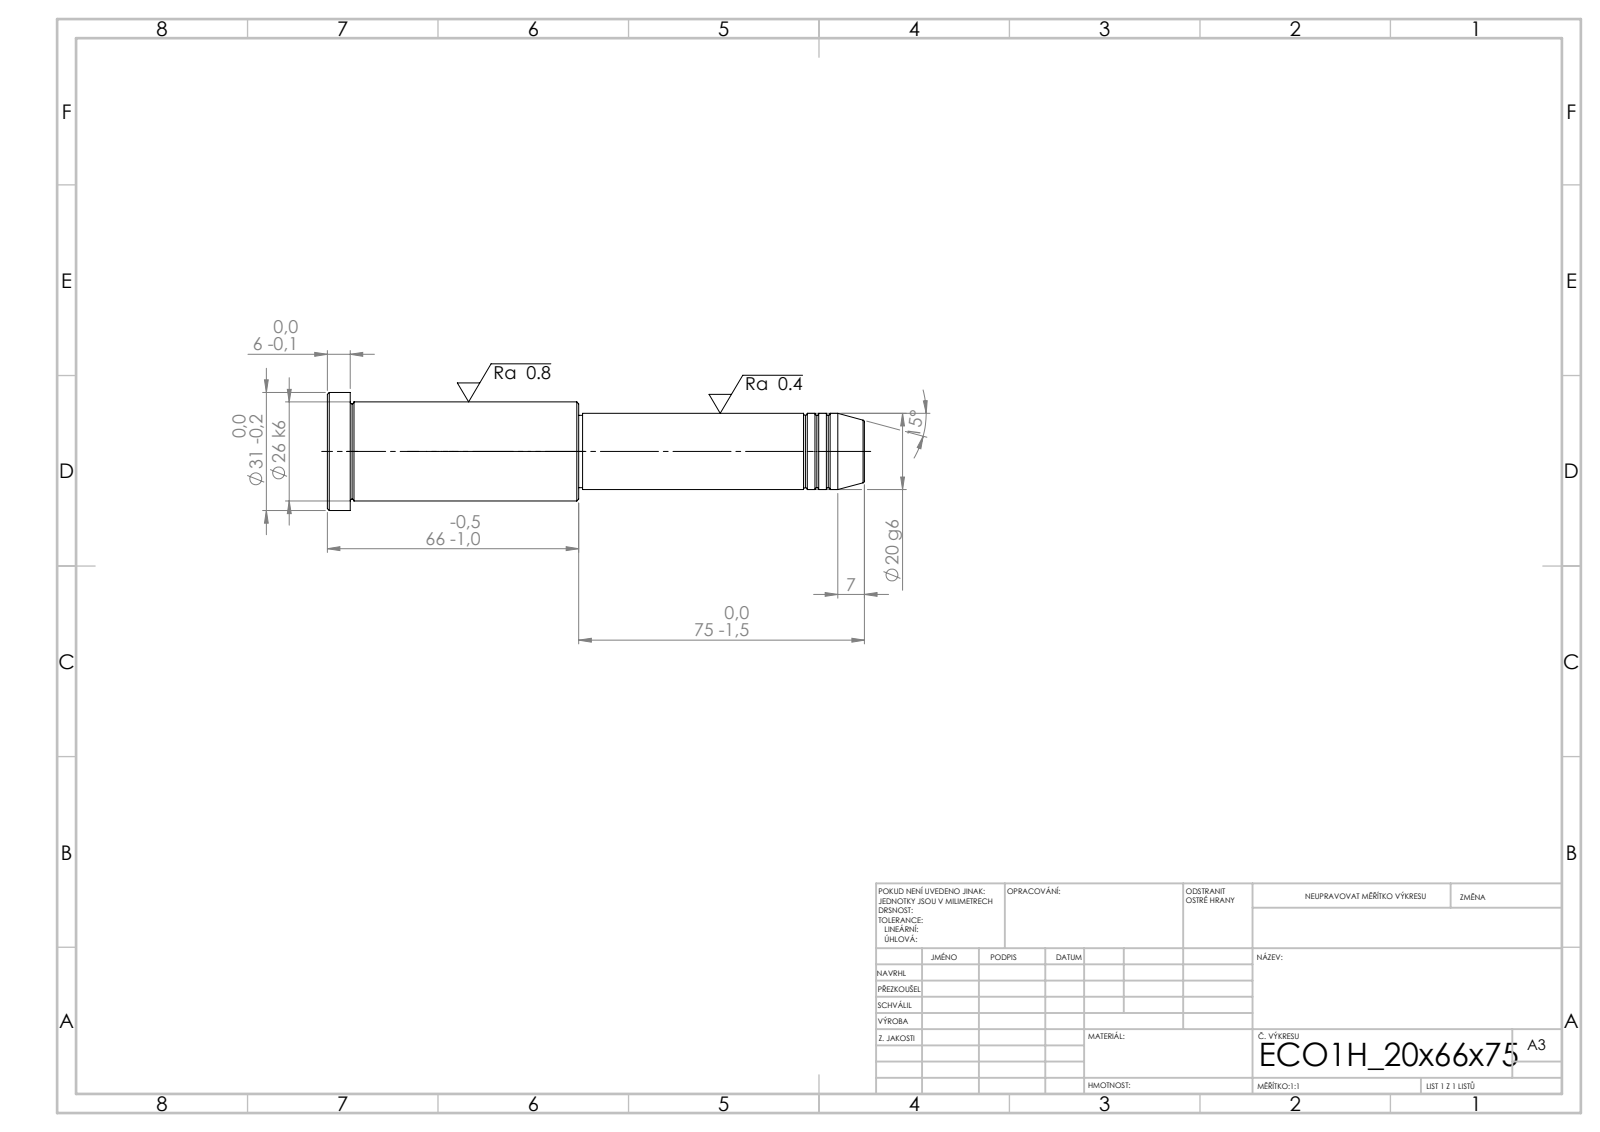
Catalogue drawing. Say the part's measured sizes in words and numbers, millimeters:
Its 3-D file was written by "SolidWorks 2019 (CONFIG_CONTROL_DESIGN)". It is 1 solid with 43 faces: 5 planar, 14 cylindrical and 24 other. Overall it measures 141 by 31 by 31 millimeters. Its volume is 59 401 cubic millimeters and its surface area 11 714 square millimeters. Round bosses or shafts: 1 of diameter 31, 1 of diameter 26, 1 of diameter 20, 1 of diameter 19. The main face-to-face distances are 6, 60, 66, 75, 135, 141, 74, 1, 61, 67.
